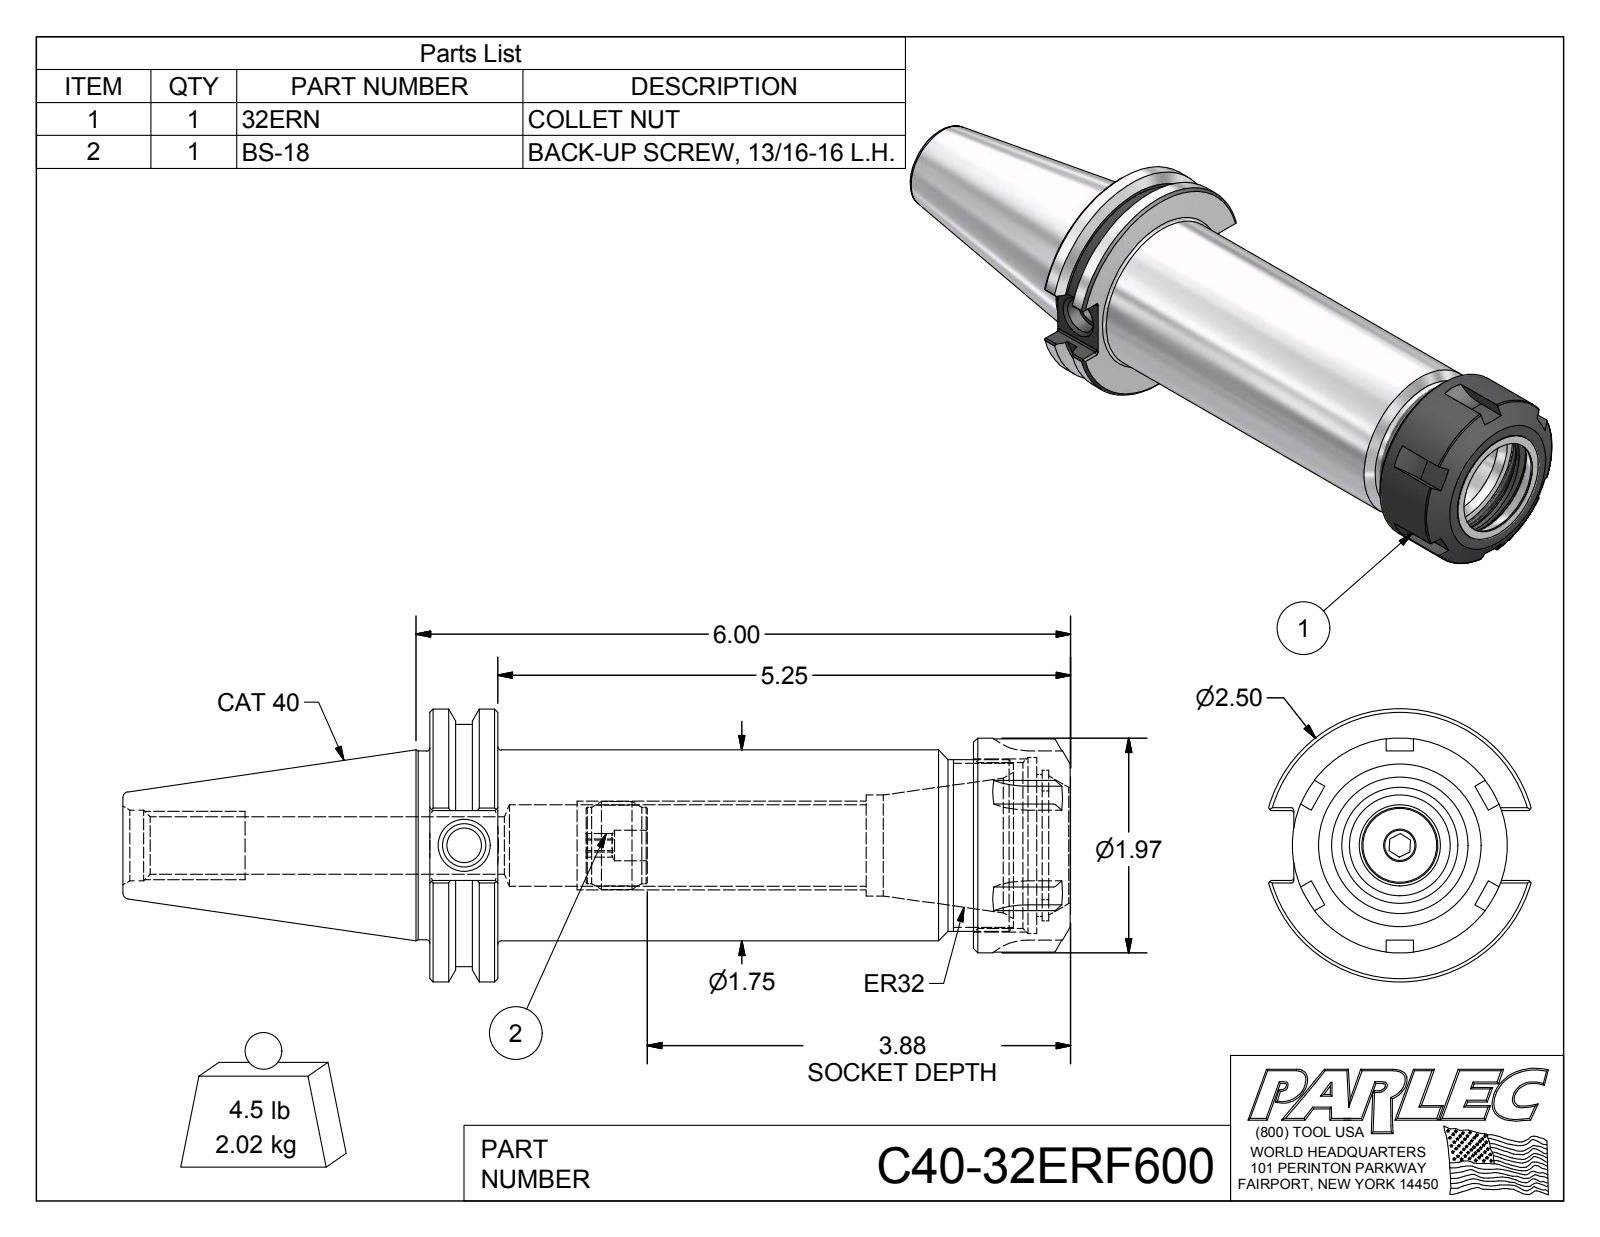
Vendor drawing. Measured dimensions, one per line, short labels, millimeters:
name: C40-32ER6-1; 32ERN; BS-18; C40-32ERF600
written by: Autodesk Inventor 2016 (AUTOMOTIVE_DESIGN)
unit: mm
bodies: 3 solids, 183 faces (75 planar, 50 cylindrical, 58 other)
size: 220.66 × 63.5 × 61.05
volume: 259 473 mm³; area: 54 553 mm²
holes: 1× ⌀7.11, 1× ⌀8, 1× ⌀10.13, 1× ⌀13.39, 1× ⌀16.46, 1× ⌀18.92, 1× ⌀23.5, 1× ⌀27, 1× ⌀33.02, 1× ⌀38.65, 1× ⌀41
bosses: 1× ⌀63.5, 1× ⌀56.36, 1× ⌀50, 1× ⌀44.45, 1× ⌀43.94, 1× ⌀40, 1× ⌀20.45, 1× ⌀17.78
rounds: 24× R0.51, 1× R14.9, 1× R17.5
face distances: 15.88, 149.23, 133.35, 126.45, 110.57, 22.78, 141.46, 125.58, 15.01, 7.77
hole spacings: 1.85
